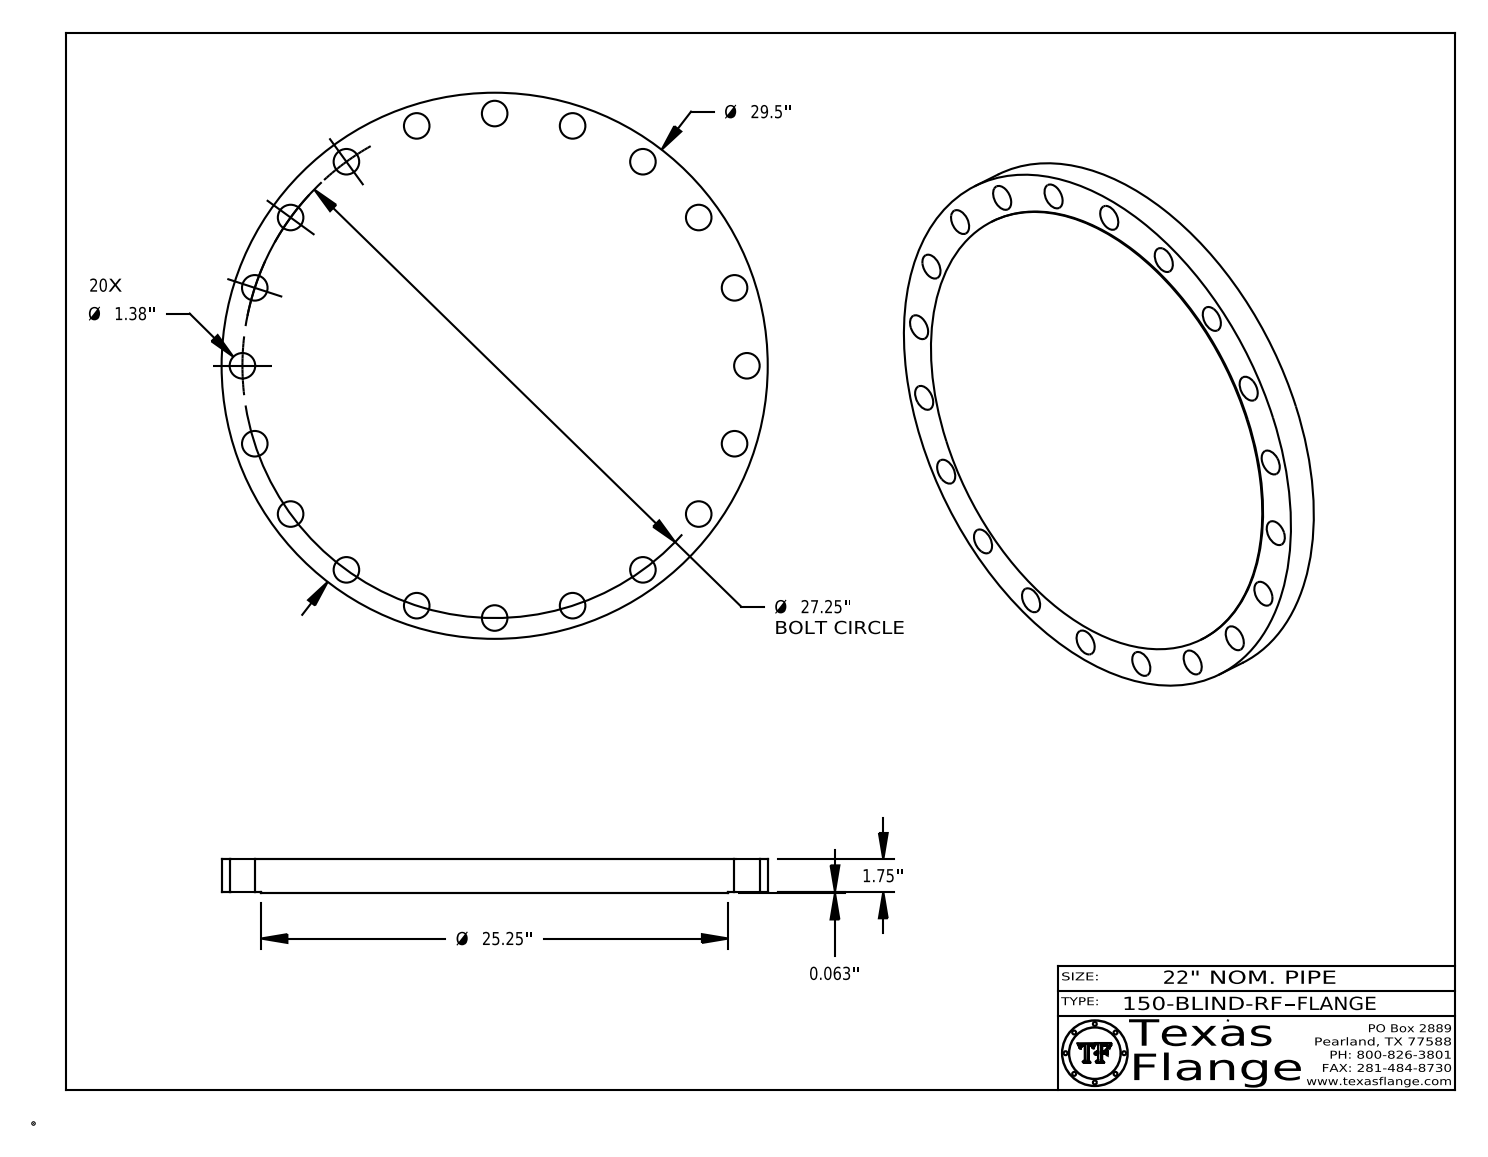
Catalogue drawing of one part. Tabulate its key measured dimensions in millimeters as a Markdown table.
| quantity | value |
| --- | --- |
| part name | 150-BLIND-RF |
| STEP written by | CATIA V5 STEP AP214 (AUTOMOTIVE_DESIGN) |
| units | millimeters |
| bodies | 1 solid, 432 faces (368 planar, 64 cylindrical, 0 other) |
| overall size | 749.3 × 749.3 × 46.1 |
| volume | 19 250 000 mm³ |
| surface area | 1 049 000 mm² |
| round holes (diameter × count) | 35.1 × 20, 12.6 × 1 |
| round bosses / shafts (diameter × count) | 0.8 × 8, 749.3 × 1, 641.4 × 1, 9.9 × 1 |
| main face-to-face distances | 46.1, 1.6, 44.5, 45.7, 44.1, 0.4, 3.8, 3.7, 0.7, 3.1 |
| hole center spacings | 489.4, 658.3, 213.9, 314.2, 108.3, 406.8, 560, 616.7 |
